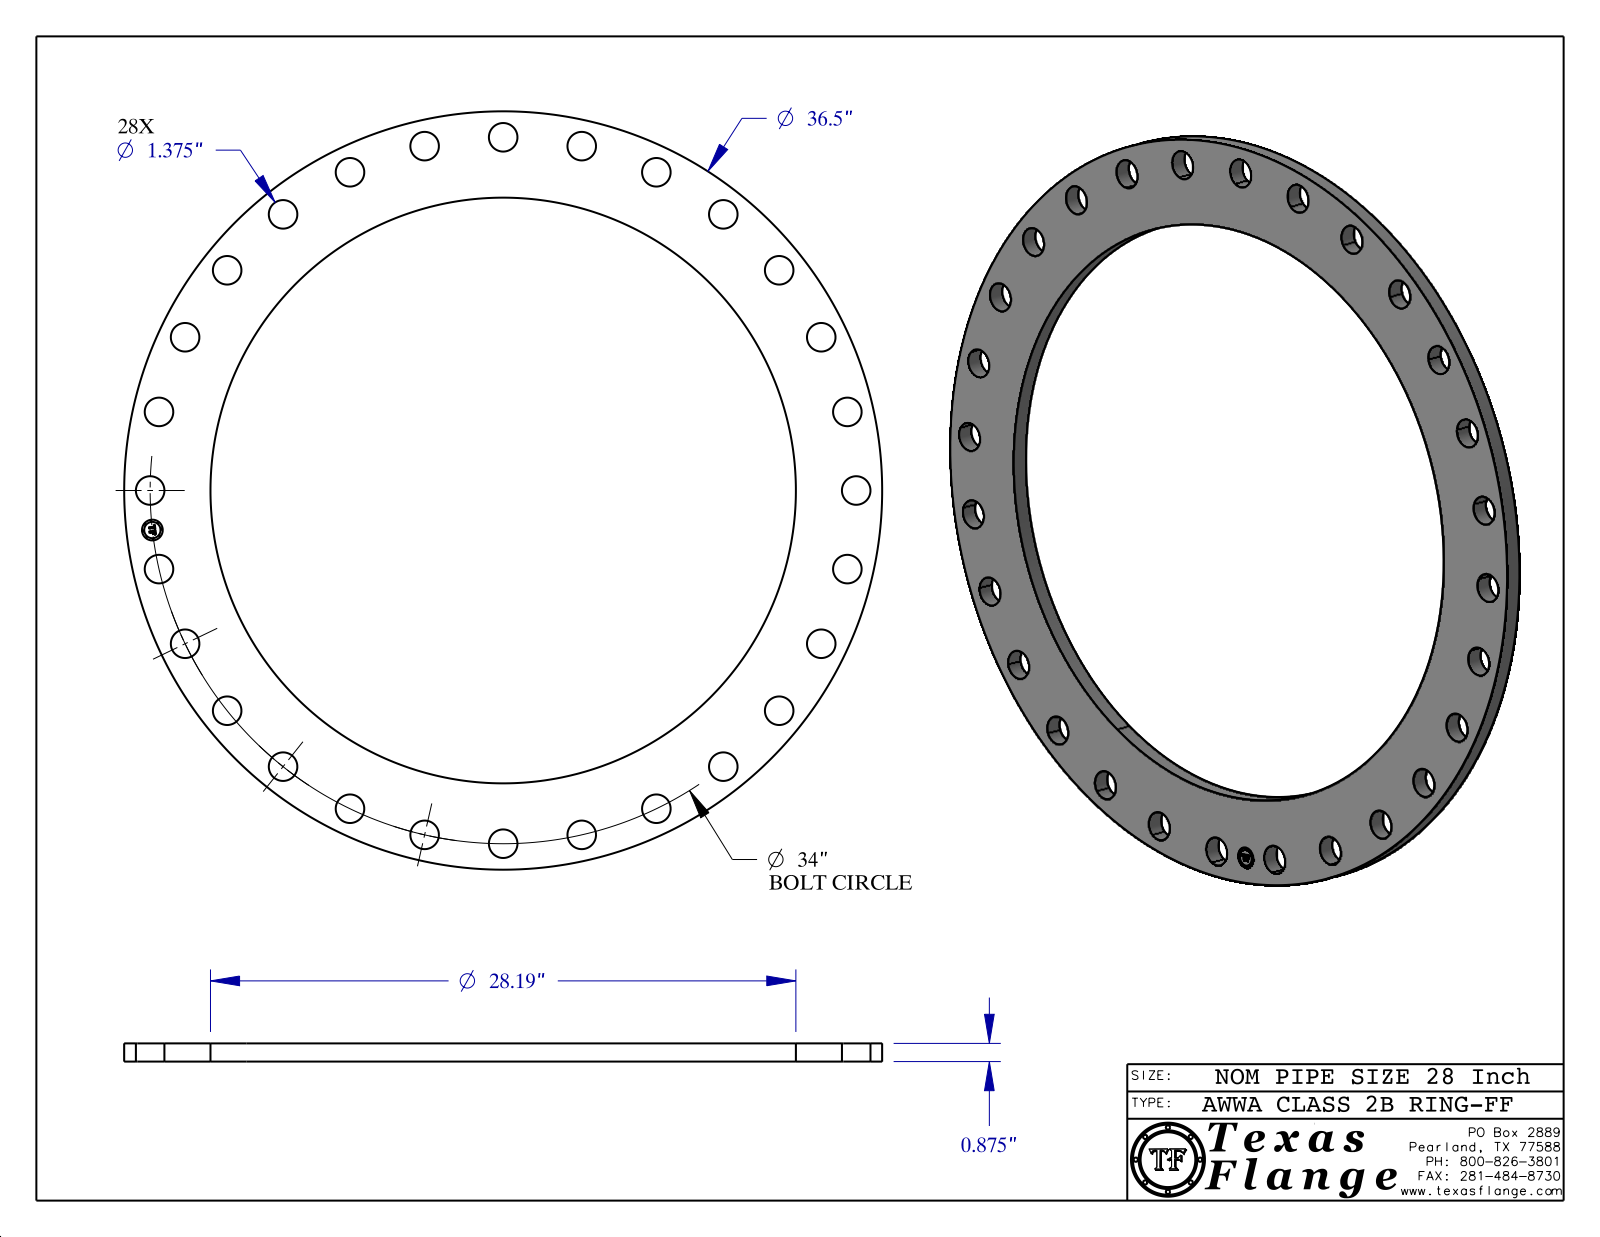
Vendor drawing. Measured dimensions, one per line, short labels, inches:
name: AWWA Class 2B-RING-FF
written by: CATIA V5 STEP AP214 (AUTOMOTIVE_DESIGN)
unit: in
bodies: 1 solid, 447 faces (367 planar, 80 cylindrical, 0 other)
size: 36.5 × 36.5 × 0.875
volume: 333 in³; area: 1 045 in²
holes: 28× ⌀1.375, 1× ⌀1, 1× ⌀28.19
bosses: 8× ⌀0.061, 1× ⌀36.5, 1× ⌀0.788
face distances: 0.875, 0.86, 0.015, 0.298, 0.293, 0.054, 0.193, 0.248, 0.044, 0.15
hole spacings: 3.807, 7.566, 30.633, 33.786, 17, 11.23, 18.089, 21.198
